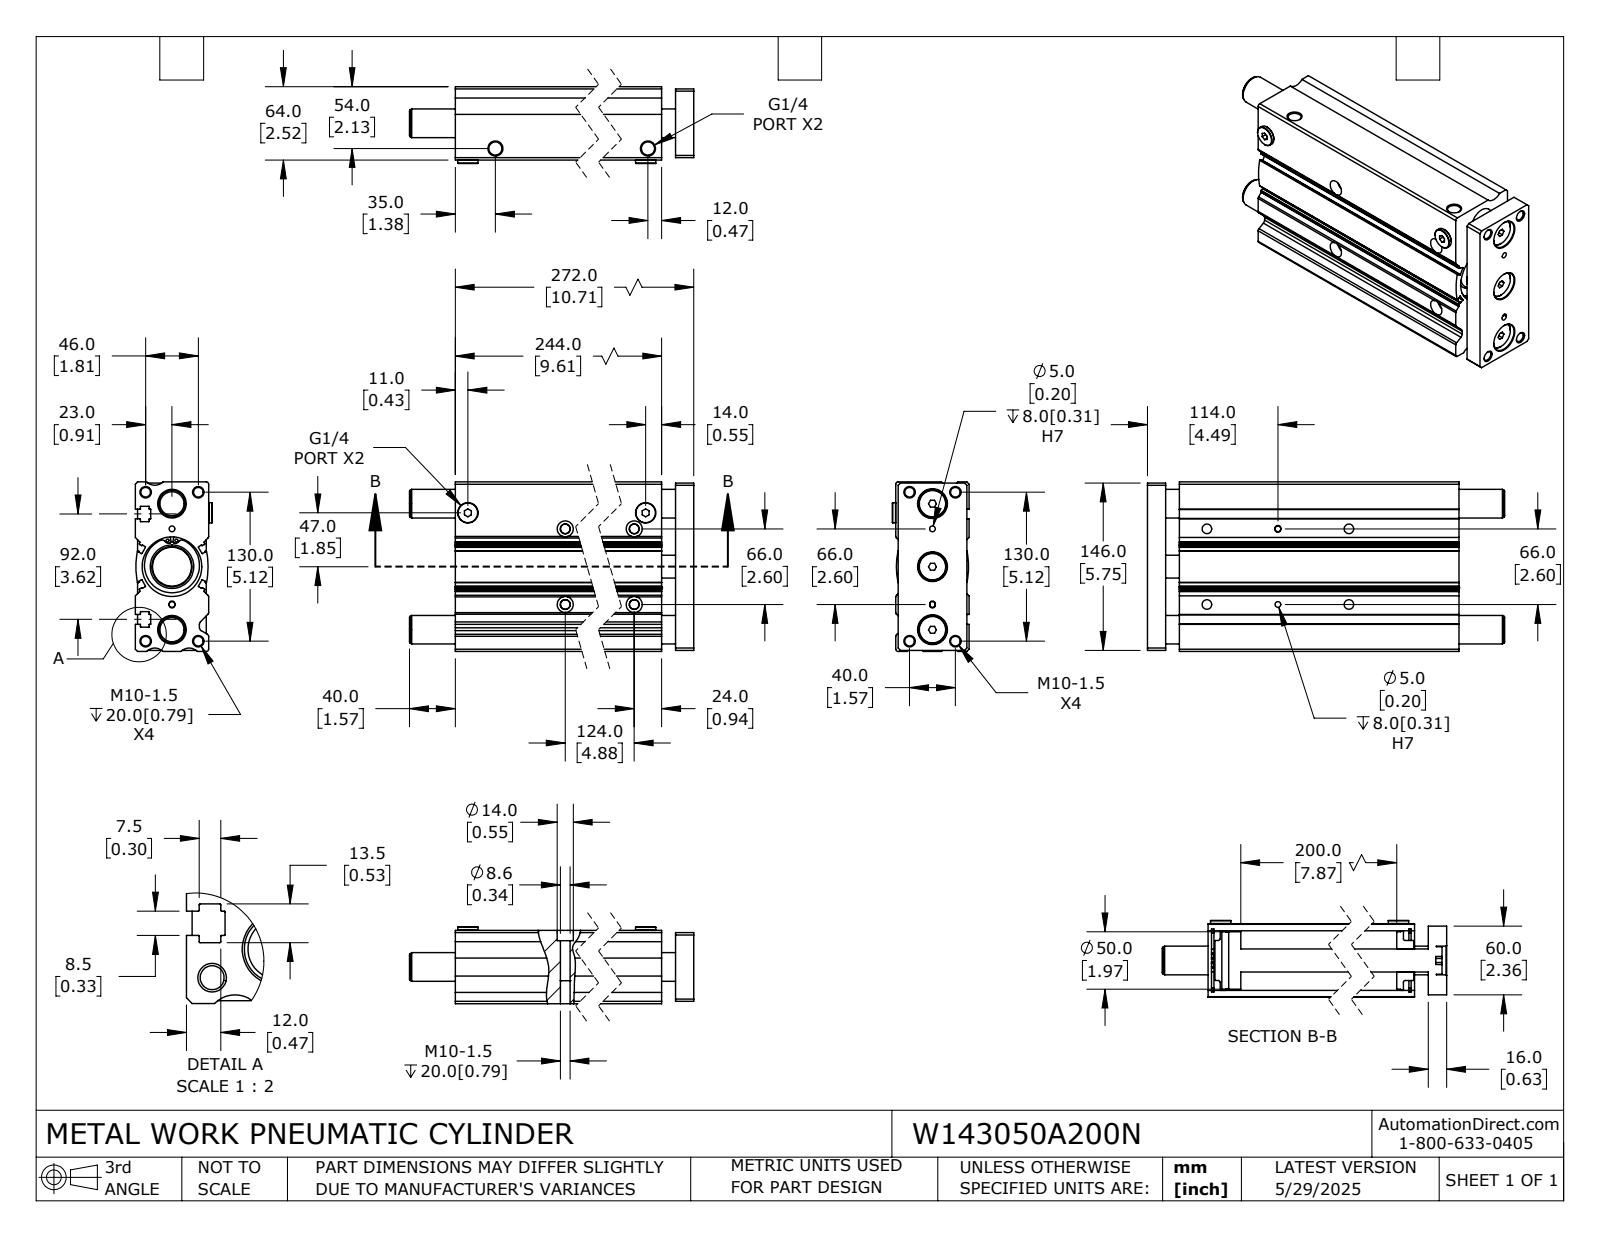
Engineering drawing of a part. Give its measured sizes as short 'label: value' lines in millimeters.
name: W143050A200N_ROD; W143050A200N; W143050A200N_BODY
written by: SolidWorks 2024 (CONFIG_CONTROL_DESIGN)
unit: mm
bodies: 6 solids, 466 faces (186 planar, 224 cylindrical, 56 other)
size: 312 × 148 × 67
volume: 1 894 000 mm³; area: 348 500 mm²
holes: 12× ⌀8.4, 4× ⌀2.5, 4× ⌀5, 4× ⌀8.6, 4× ⌀14, 3× ⌀25, 2× ⌀11.5, 2× ⌀48, 1× ⌀20
bosses: 3× ⌀24, 2× ⌀17.7, 1× ⌀55, 1× ⌀52, 1× ⌀50, 1× ⌀35
rounds: 44× R0.3, 12× R0.5, 10× R3, 6× R2, 6× R68, 4× R1, 4× R2.5, 3× R10
face distances: 64, 12, 148, 2.5, 13.5, 244, 16, 256, 92, 2
hole spacings: 3, 10.8, 22.1, 22.4, 23.3, 24.5, 25.1, 32.3
